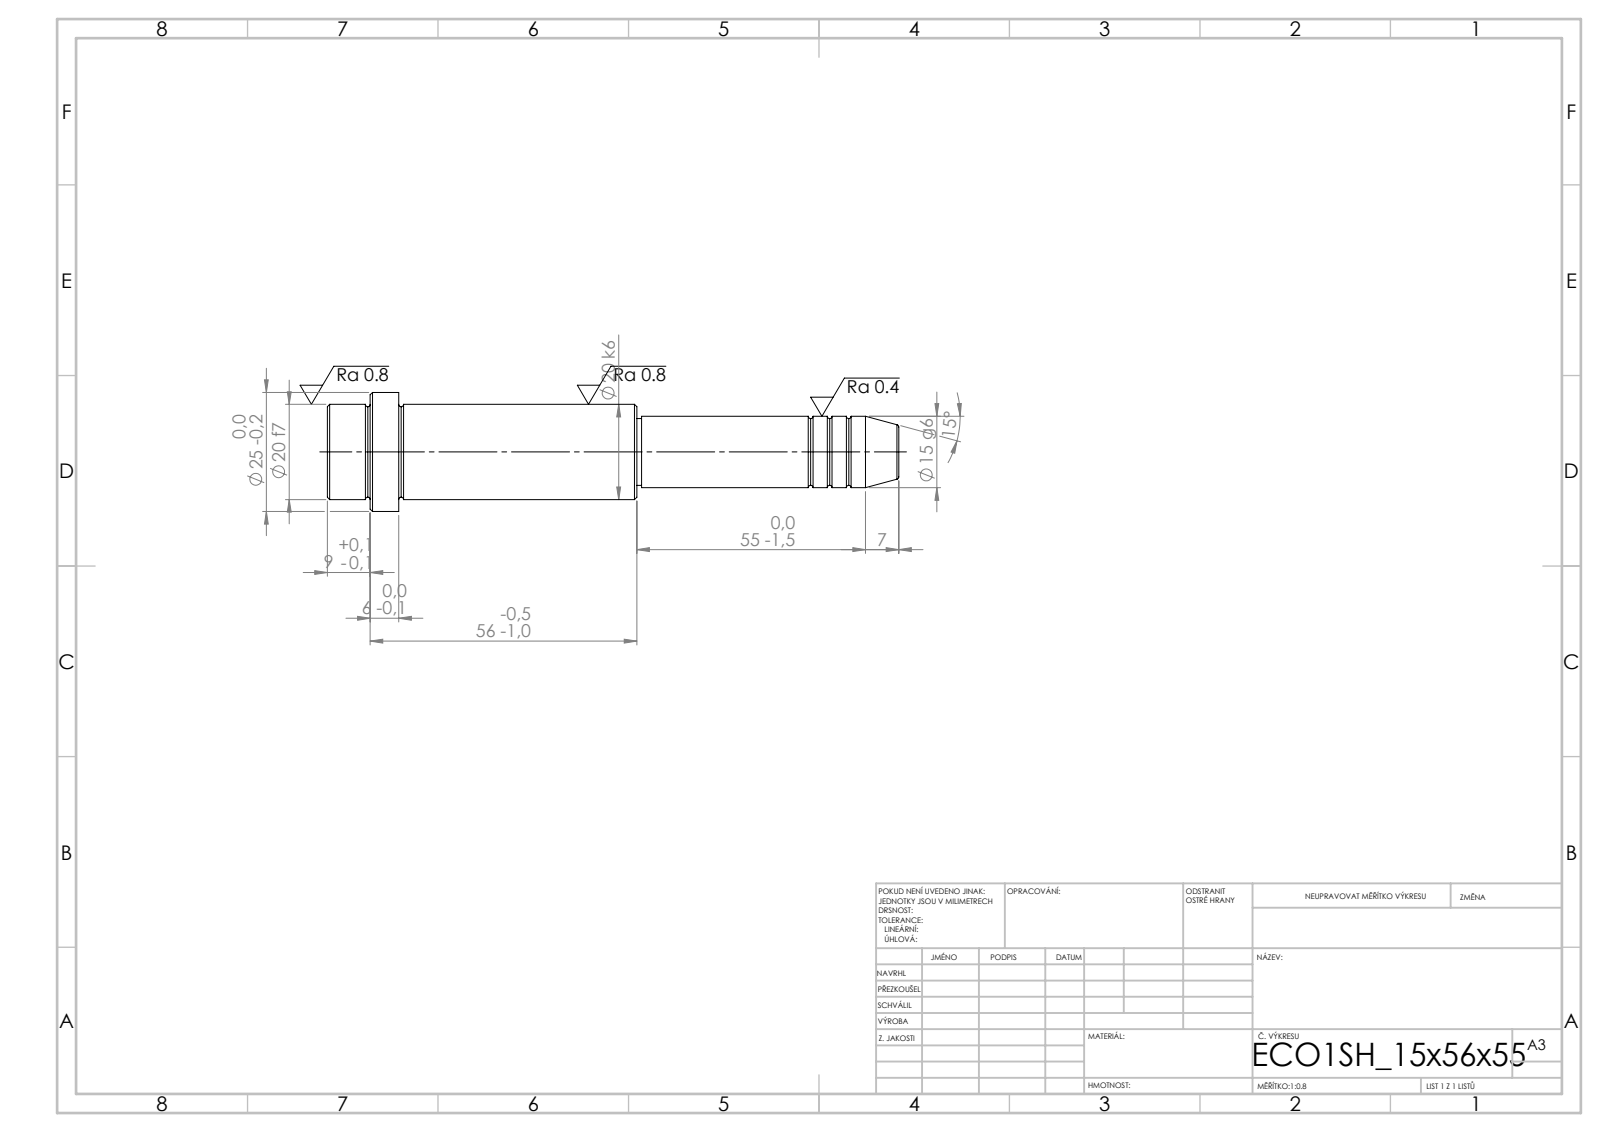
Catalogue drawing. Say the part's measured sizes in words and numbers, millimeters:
Its 3-D file was written by "SolidWorks 2019 (CONFIG_CONTROL_DESIGN)". It is 1 solid with 52 faces: 6 planar, 16 cylindrical and 30 other. Overall it measures 120 by 25 by 25 millimeters. Its volume is 30 765 cubic millimeters and its surface area 7 758 square millimeters. Round bosses or shafts: 1 of diameter 25, 1 of diameter 20, 1 of diameter 15, 1 of diameter 14. The main face-to-face distances are 15, 6, 9, 50, 56, 65, 55, 105, 111, 120.
